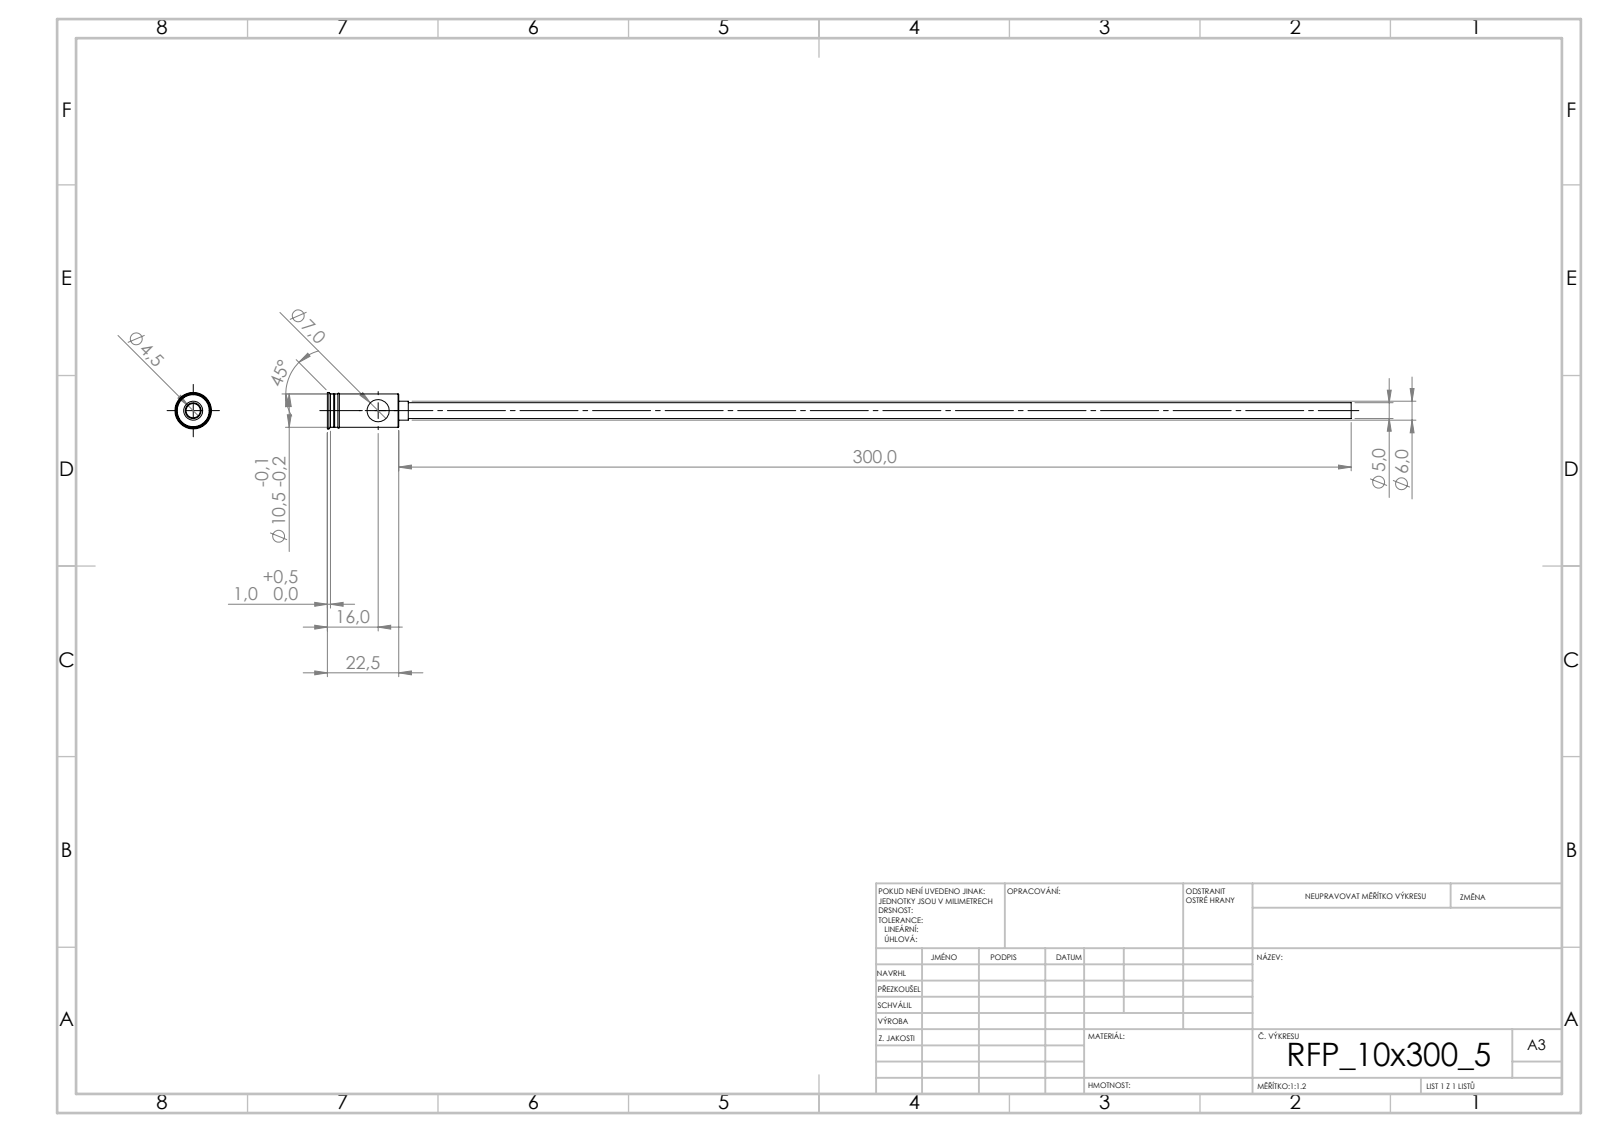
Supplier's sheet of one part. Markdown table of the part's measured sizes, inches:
| quantity | value |
| --- | --- |
| STEP written by | SolidWorks 2019 (CONFIG_CONTROL_DESIGN) |
| units | inches |
| bodies | 1 solid, 44 faces (20 planar, 16 cylindrical, 8 other) |
| overall size | 12.697 × 0.453 × 0.453 |
| volume | 0.16 in³ |
| surface area | 15.66 in² |
| round holes (diameter × count) | 0.177 × 1, 0.276 × 1 |
| round bosses / shafts (diameter × count) | 0.453 × 1, 0.413 × 1, 0.236 × 1, 0.197 × 1 |
| main face-to-face distances | 0.886, 0.807, 0.079, 0.232, 0.795, 0.091, 0.118, 0.913, 0.925, 1.004 |
